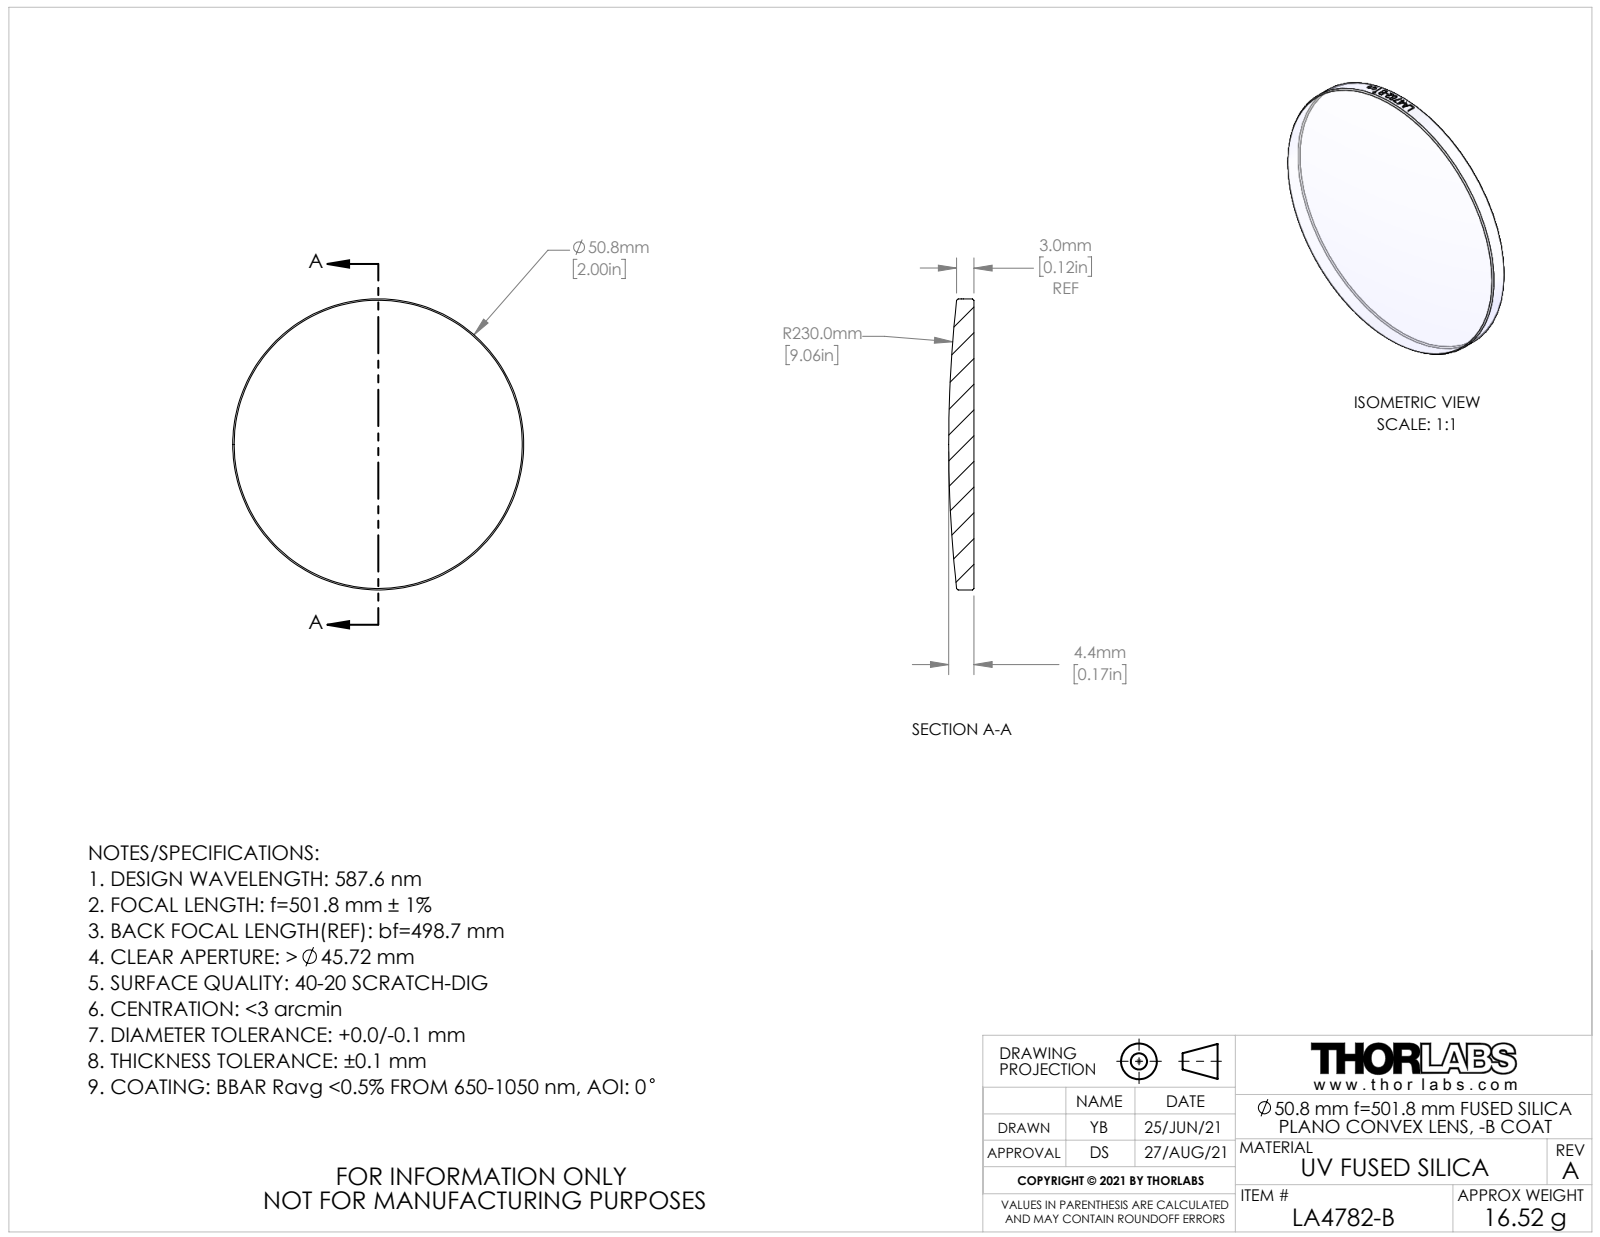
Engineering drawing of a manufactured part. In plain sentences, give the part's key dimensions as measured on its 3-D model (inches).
The part is named "CTN017910-E0W". Its 3-D file was written by "SolidWorks 2018 (AUTOMOTIVE_DESIGN)". It is 1 solid with 27 faces: 1 planar, 20 cylindrical and 6 other. Overall it measures 2 by 2 by 0.174 inches. Its volume is 0.458 cubic inches and its surface area 6.967 square inches. Round bosses or shafts: 1 of diameter 2.
